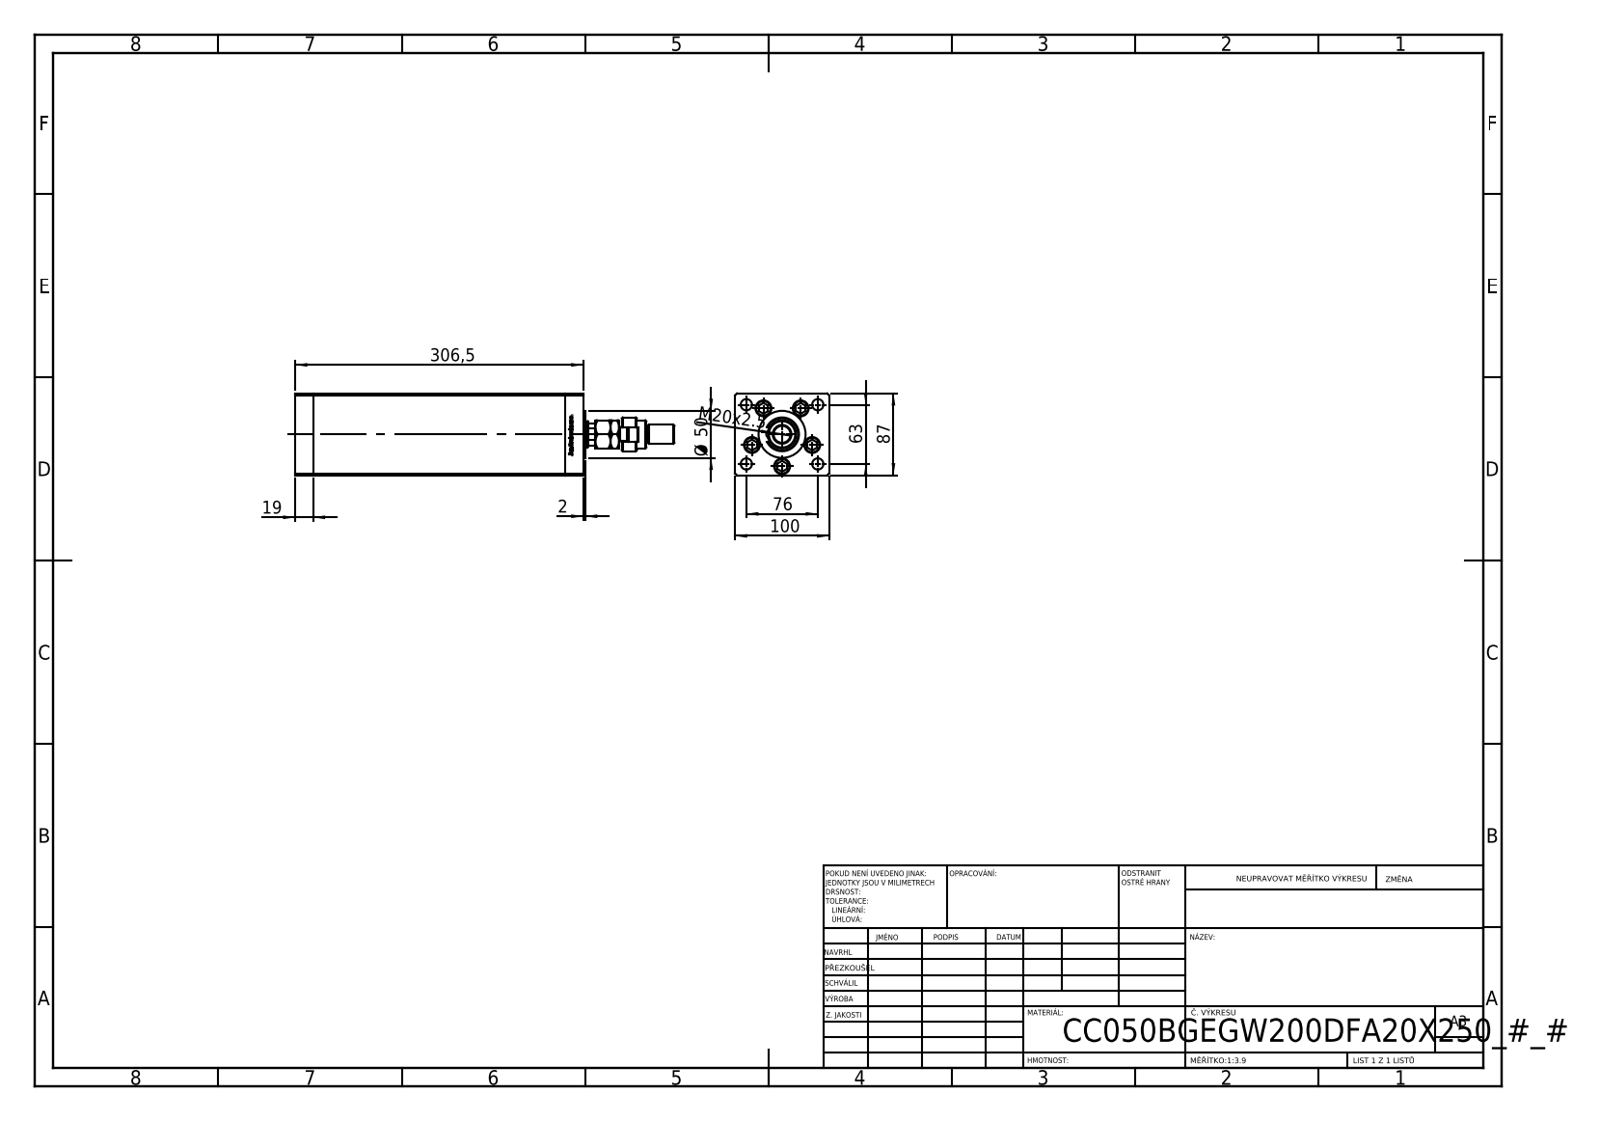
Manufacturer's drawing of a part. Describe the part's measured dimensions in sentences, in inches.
The part is named "V220C_B MIDDLE; V220C_FRONT_B; V220C BACK_B; FEMALE_PART_FOR_DFA (+3 more)". Its 3-D file was written by "SolidWorks 2019 (CONFIG_CONTROL_DESIGN)". It is 16 solids with 1270 faces: 492 planar, 160 cylindrical and 618 other. Overall it measures 15.886 by 3.937 by 3.425 inches. Its volume is 142.7 cubic inches and its surface area 457.6 square inches. Round holes: 7 of diameter 0.531, 5 of diameter 0.669, 4 of diameter 0.472, 2 of diameter 0.079, 2 of diameter 0.518, 1 of diameter 0.728, 1 of diameter 1.102. Round bosses or shafts: 5 of diameter 0.315, 2 of diameter 0.669, 1 of diameter 1.969, 1 of diameter 1.417, 1 of diameter 1.181, 1 of diameter 0.866, 1 of diameter 0.787, 1 of diameter 0.709. Partial cylindrical surfaces (rounded edges, fillets, slot ends): 2 of radius 0.037, 1 of radius 0.295, 1 of radius 0.472, 1 of radius 0.531. The main face-to-face distances are 3.937, 3.425, 0.748, 10.571, 11.319, 1.348, 12.067, 0.6, 9.97, 10.719. The hole center spacings are 1.339, 0.732, 1.561, 1.943, 2.281, 0.828, 1.499, 1.546.
